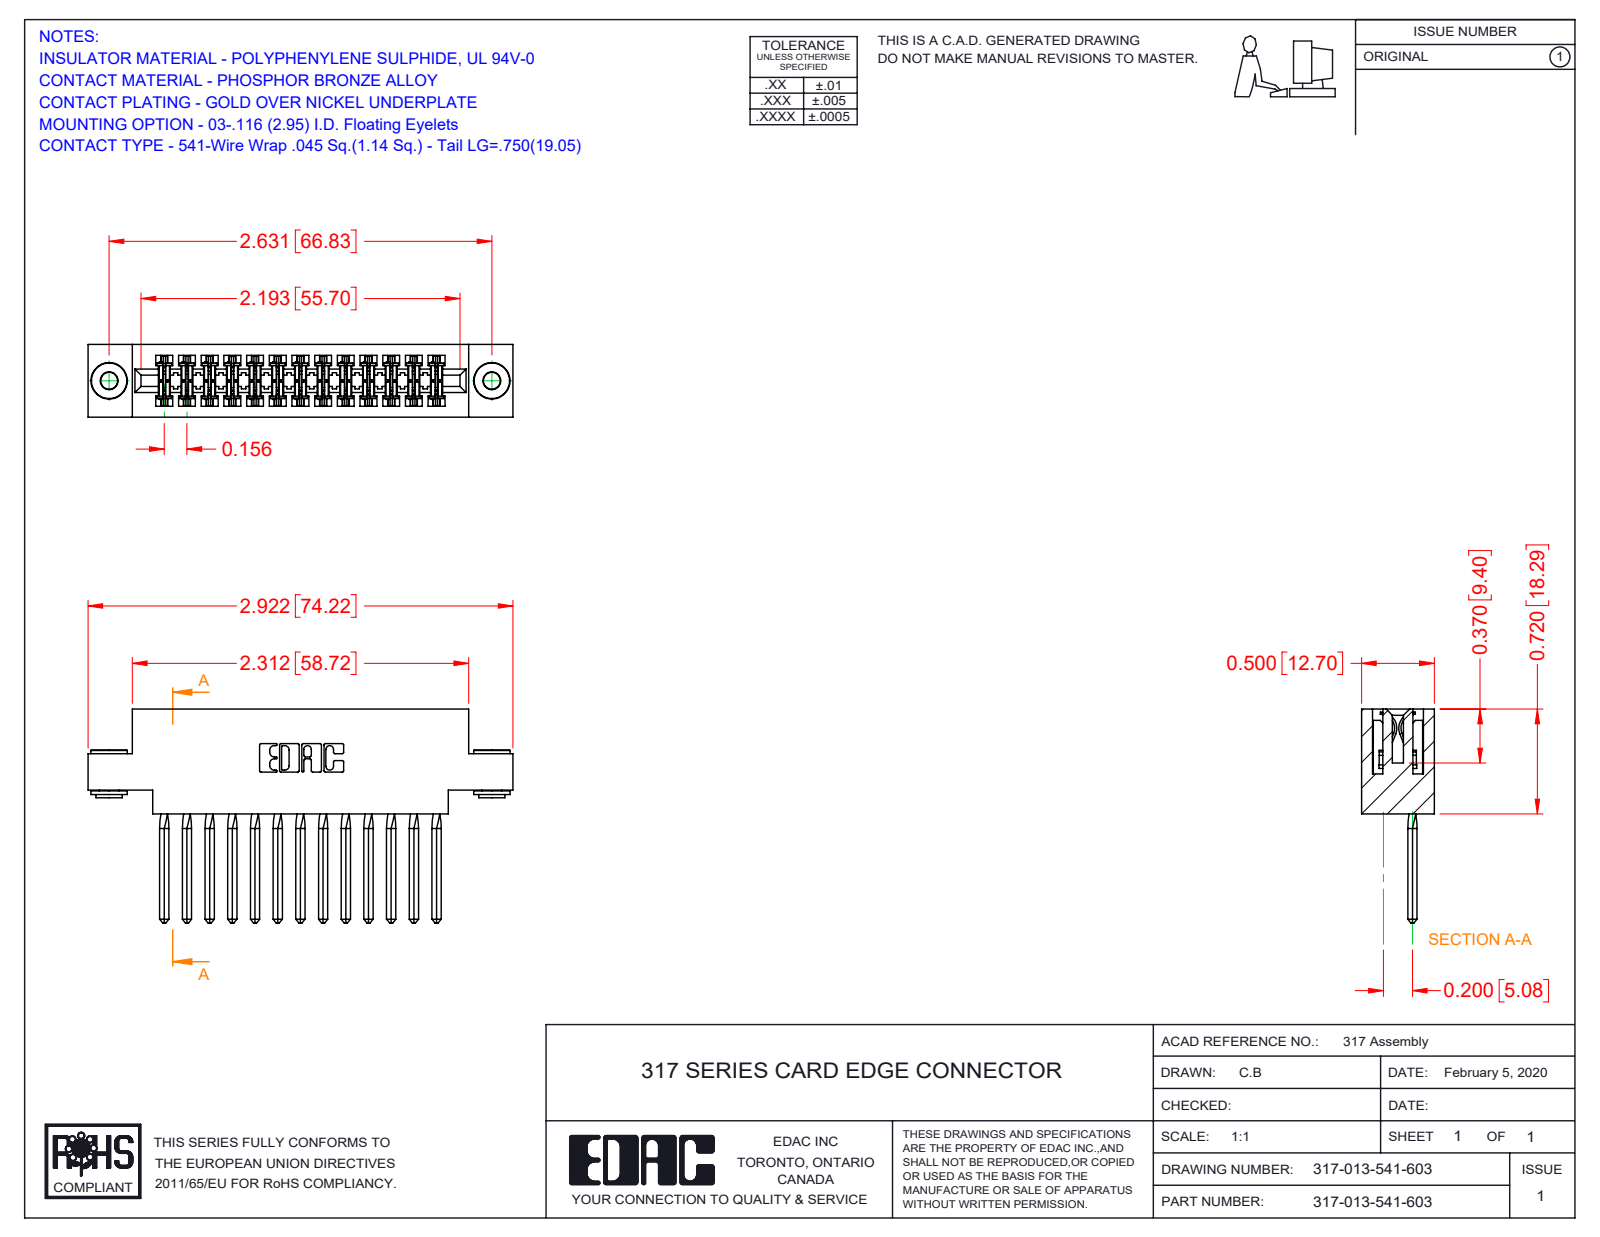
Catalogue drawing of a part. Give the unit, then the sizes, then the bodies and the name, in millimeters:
Units: millimetres
Overall size (bounding box): 74.2 × 37.3 × 12.7
Round holes (diameter × count): ⌀2.9 ×2, ⌀4 ×2
Round bosses / shafts (diameter × count): ⌀6.4 ×2, ⌀4.6 ×2, ⌀3.5 ×2
Partial cylindrical surfaces — rounded edges, fillets, slot ends (radius × count): R0.4 ×26, R0.3 ×22, R0.2 ×6, R0.8 ×6, R0.7 ×3, R2.4 ×2, R2.5 ×2, R2.8 ×2
Main face-to-face distances: 12.7, 1.9, 10.8, 2.8, 5.6, 1.7, 8.9, 8.4, 5, 7.7
Hole centre spacings: 66.8
Volume: 11 200 mm³ · Surface area: 15 030 mm²
Bodies: 16 solids, 2116 faces (1680 planar, 376 cylindrical, 60 other)
Part name (STEP PRODUCT): 317 Part_.156 Dia - TH; 345-250-002_345-250-002-102; 317-290-002_541; 317-013-541-603
STEP written by: SolidWorks 2016 (CONFIG_CONTROL_DESIGN)
